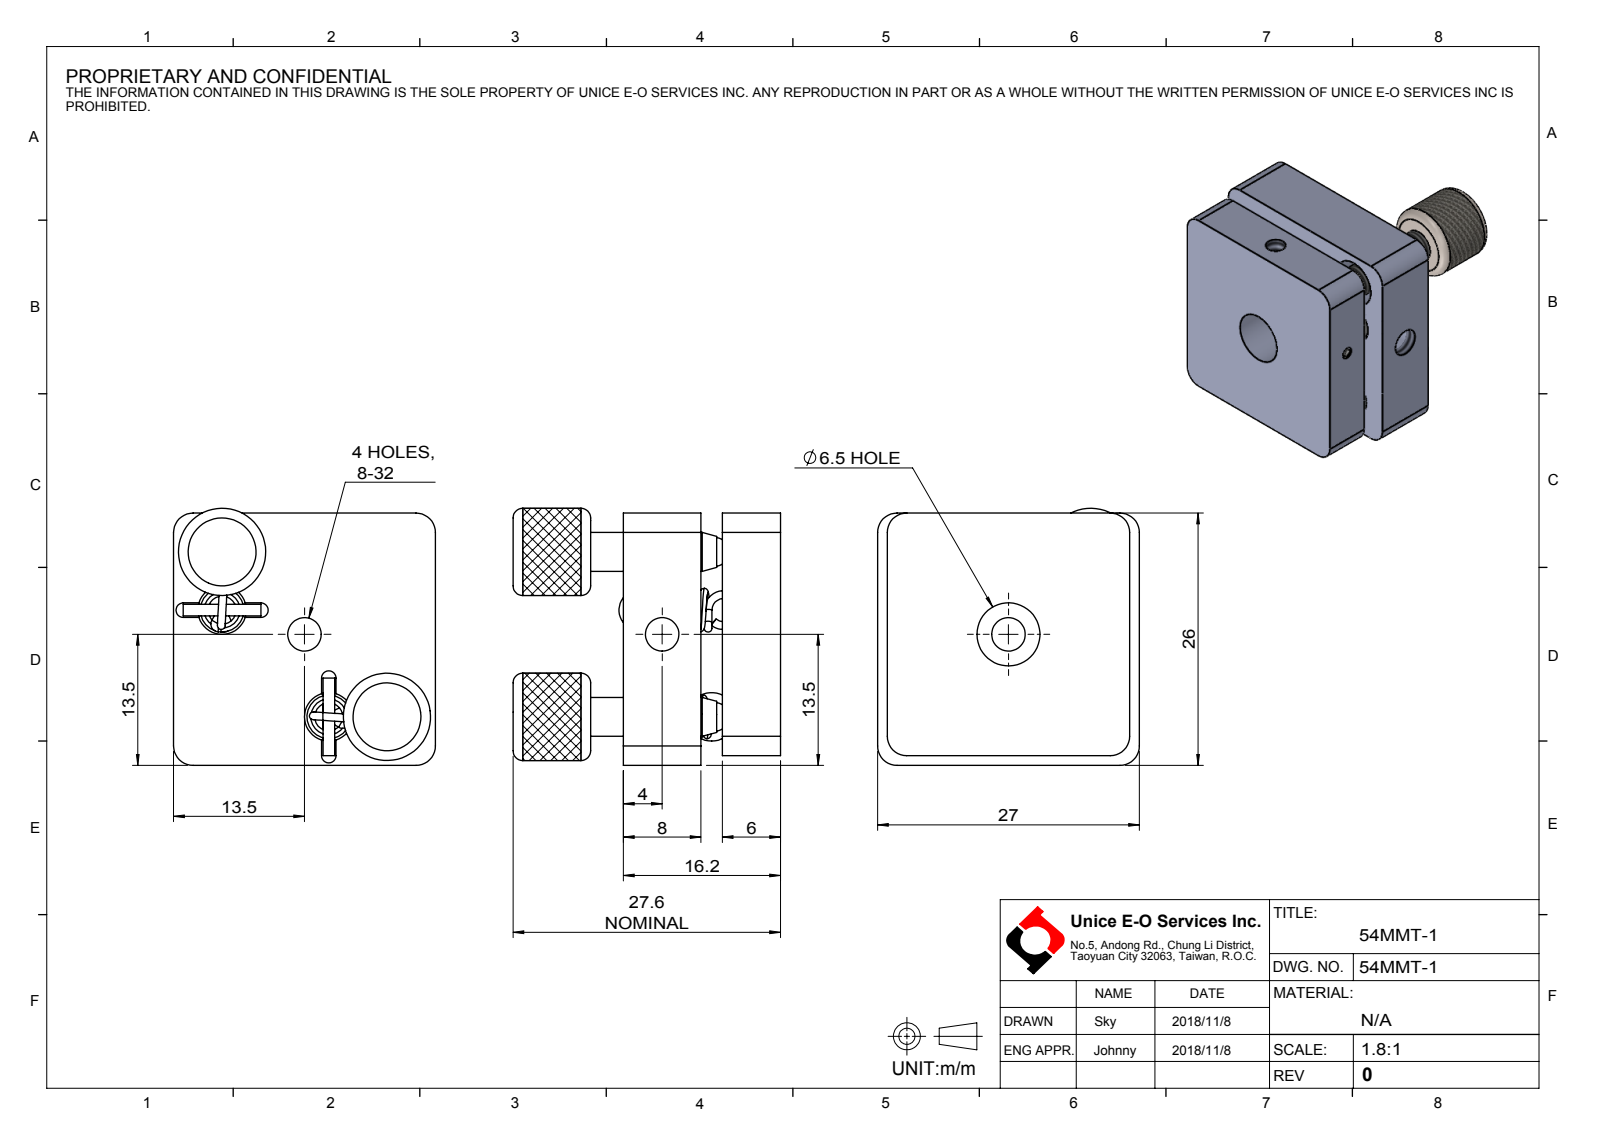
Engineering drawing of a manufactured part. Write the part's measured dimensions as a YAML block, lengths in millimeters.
part_name: "54MMT-1"
step_written_by: "SolidWorks 2016 (AUTOMOTIVE_DESIGN)"
units: millimeters
bodies: {solids: 0, faces: 142, planar: 48, cylindrical: 62, other: 32}
overall_size: [27.58, 27, 26.5]
round_holes:
  - {diameter: 0.8, count: 3}
  - {diameter: 3.45, count: 3}
  - {diameter: 1.5, count: 2}
  - {diameter: 5, count: 2}
  - {diameter: 6, count: 2}
  - {diameter: 2.5, count: 1}
  - {diameter: 6.5, count: 1}
round_bosses_or_shafts:
  - {diameter: 1.2, count: 4}
  - {diameter: 9, count: 2}
  - {diameter: 4, count: 2}
  - {diameter: 1.5, count: 2}
partial_cylinders:
  - {radius: 2, count: 8}
  - {radius: 0.75, count: 7}
  - {radius: 1.25, count: 1}
face_to_face_distances: [8, 16.2, 8.2, 6, 10.2, 2.2, 26, 1, 25, 27]
hole_center_spacings: [6, 8.86, 9.53, 12.02, 20.25, 2.5, 3.99, 9.2]
